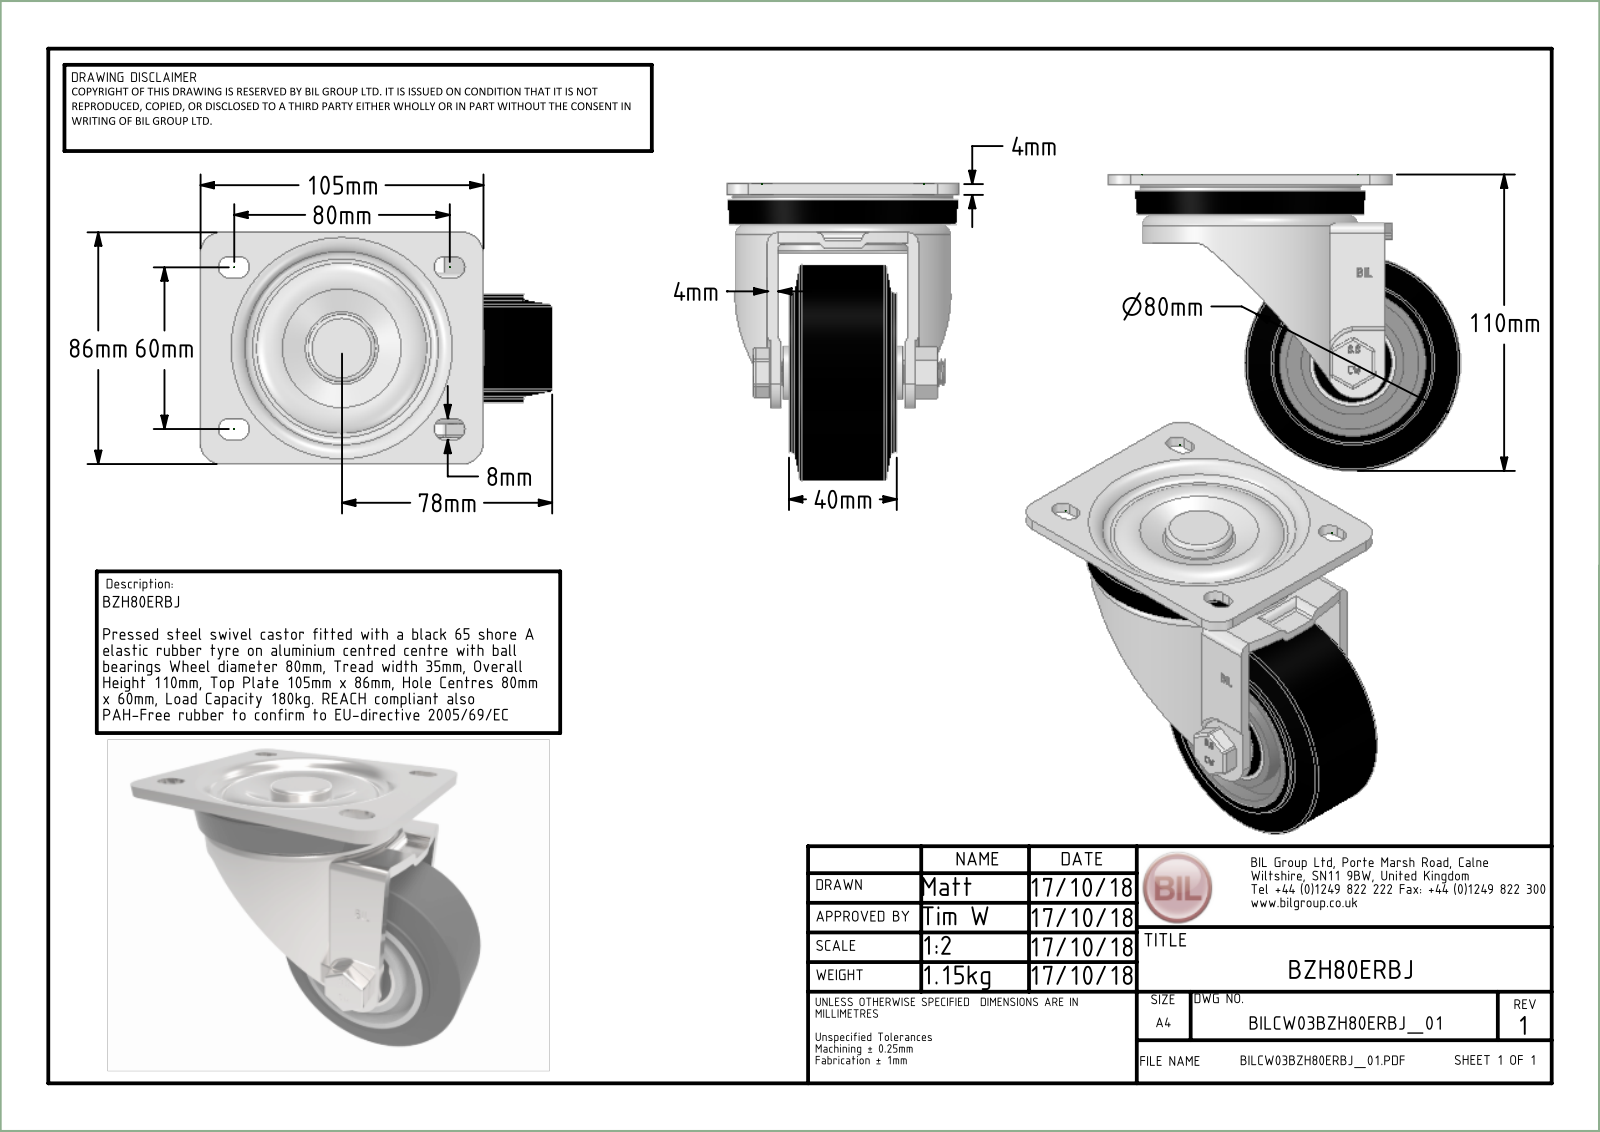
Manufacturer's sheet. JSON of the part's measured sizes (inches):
{"part_name": "BZH80ERBJ v3; BZH80AS - 2 - 44 v1; BZH80AS - 2 v2 (1); ZINC PLATED, PRESSED STEEL TOP PLATE (1) (+8 more)", "step_written_by": "Autodesk Translation Framework v14.4.0.0 (AUTOMOTIVE_DESIGN)", "units": "inches", "bodies": {"solids": 39, "faces": 1131, "planar": 412, "cylindrical": 194, "other": 525}, "overall_size": [5.138, 4.331, 3.425], "volume_in3": 18.55, "surface_area_in2": 184.1, "round_holes": [[1.26, 2], [0.394, 1], [0.402, 1], [0.413, 1], [0.472, 1], [0.591, 1], [0.807, 1], [0.984, 1], [1.055, 1], [1.102, 1], [1.11, 1], [2.106, 1]], "round_bosses_or_shafts": [[3.15, 2], [0.787, 2], [2.303, 1], [1.988, 1], [1.22, 1], [0.846, 1], [0.748, 1], [0.63, 1]], "partial_cylinders_radius": [[0.02, 18], [0.177, 8], [0.03, 6], [0.079, 4], [0.315, 4], [0.157, 2], [0.964, 2], [0.449, 1]], "face_to_face_distances": [0.157, 0.079, 0.453, 0.295, 0.236, 1.654, 1.89, 1.811, 1.575, 0.551]}
